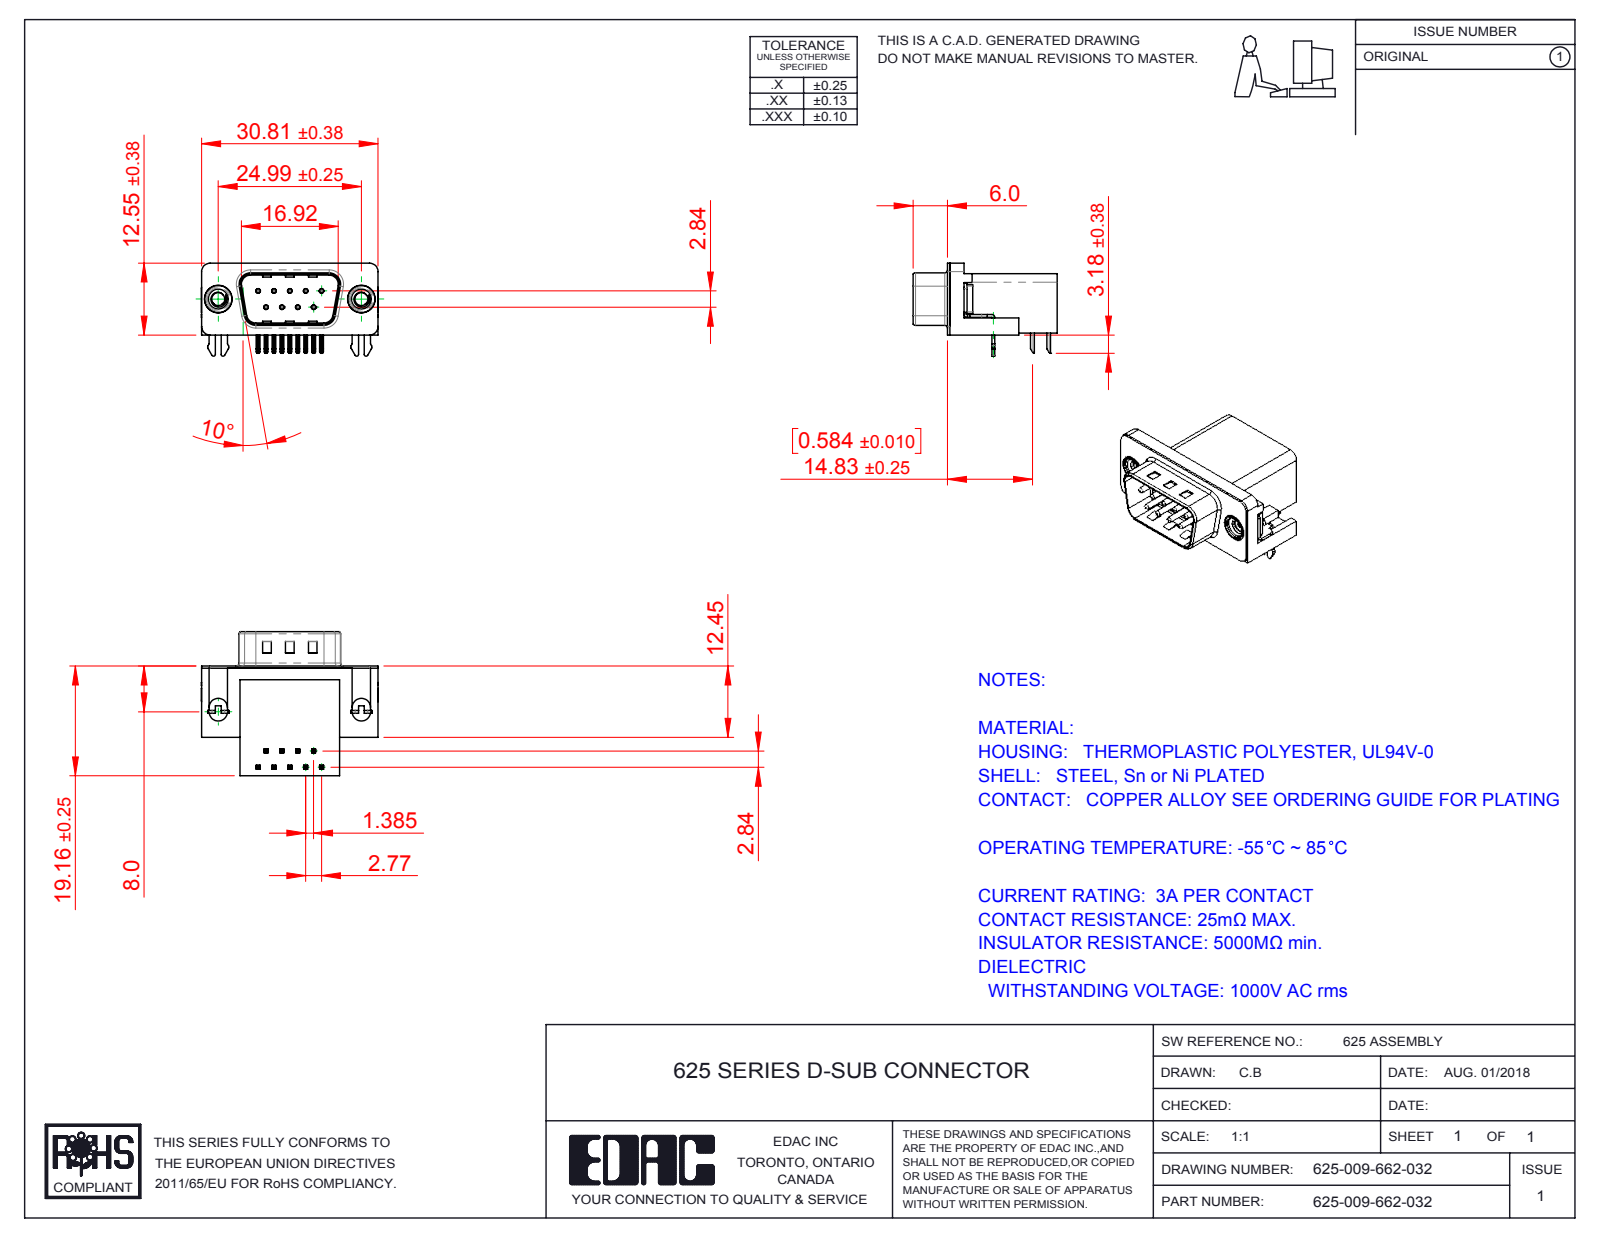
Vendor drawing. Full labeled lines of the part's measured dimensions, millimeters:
Part name (STEP PRODUCT): 625 Contact Bottom; 625 2 Prong Board Lock; 625-009-662-032; 625 4-40 Threaded Rivet (+3 more)
STEP written by: SolidWorks 2016 (CONFIG_CONTROL_DESIGN)
Units: millimetres
Bodies: 15 solids, 1033 faces (605 planar, 325 cylindrical, 103 other)
Overall size (bounding box): 30.89 × 25.16 × 16.25
Volume: 4 476 mm³ · Surface area: 4 957 mm²
Round holes (diameter × count): ⌀0.35 ×9, ⌀0.8 ×9, ⌀2.26 ×2, ⌀4 ×2, ⌀4.8 ×2, ⌀5 ×2
Round bosses / shafts (diameter × count): ⌀0.75 ×9, ⌀4.9 ×2, ⌀4.75 ×2, ⌀3.9 ×2
Partial cylindrical surfaces — rounded edges, fillets, slot ends (radius × count): R0.25 ×44, R0.12 ×18, R1 ×16, R0.5 ×14, R1.5 ×8, R1.6 ×8, R0.32 ×4, R0.9 ×4
Main face-to-face distances: 0.4, 10.34, 18.76, 19.16, 16.26, 2.5, 2.9, 0.35, 10.69, 0.5
Hole centre spacings: 3.16, 2.77, 5.54, 5.03, 5.04, 8.31, 7.48, 7.49
